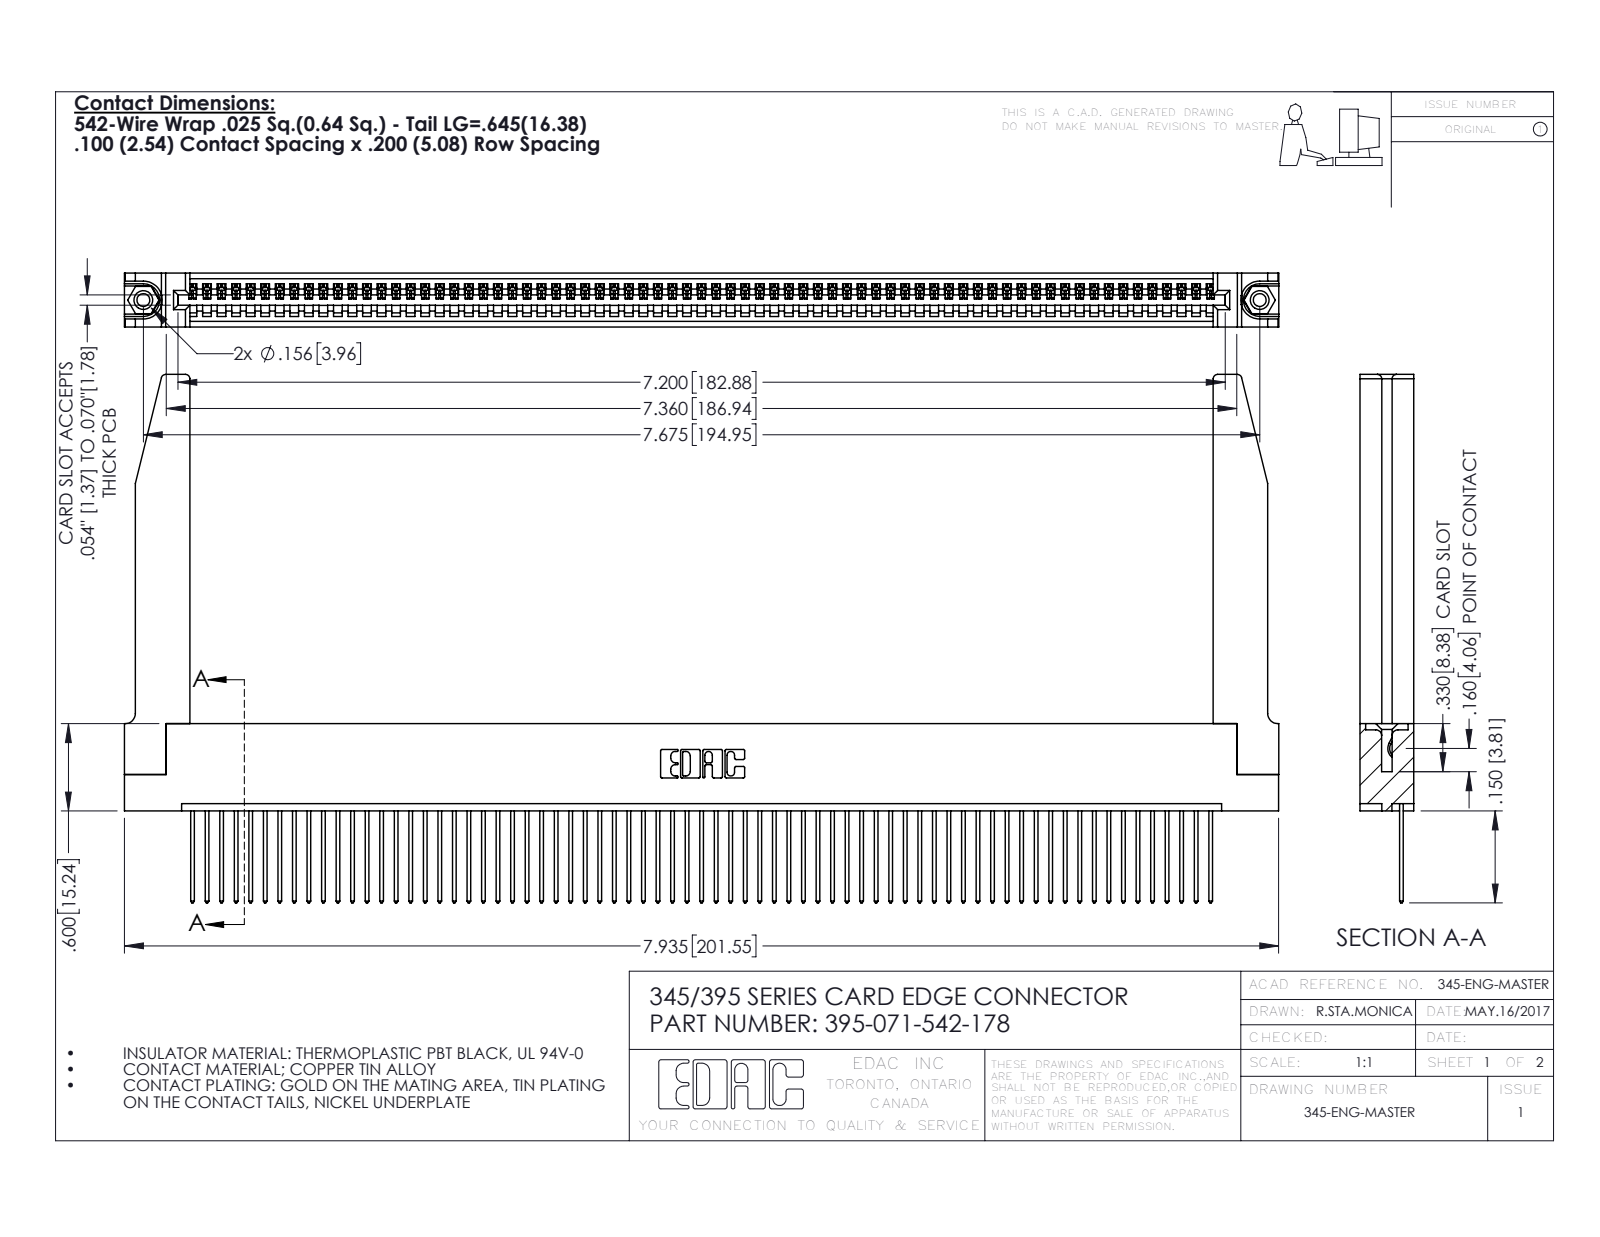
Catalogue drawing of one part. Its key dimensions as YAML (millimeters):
part_name: "345-220-078_345-220-078; 345-250-001_345-250-001-102; 395-071-542-178; 345-292-001_345-293-142 (+1 more)"
step_written_by: "SolidWorks 2016 (CONFIG_CONTROL_DESIGN)"
units: millimeters
bodies: {solids: 76, faces: 4478, planar: 3062, cylindrical: 1364, other: 52}
overall_size: [201.6, 92.3, 9.4]
volume: 27320
surface_area: 34210
round_holes:
  - {diameter: 2.3, count: 2}
  - {diameter: 3.2, count: 2}
  - {diameter: 4, count: 2}
  - {diameter: 1.6, count: 1}
round_bosses_or_shafts:
  - {diameter: 3.9, count: 2}
partial_cylinders:
  - {radius: 0.2, count: 142}
  - {radius: 0.3, count: 142}
  - {radius: 0.3, count: 22}
  - {radius: 0.8, count: 8}
  - {radius: 0.2, count: 6}
  - {radius: 0.8, count: 6}
  - {radius: 0.7, count: 3}
  - {radius: 0.8, count: 2}
face_to_face_distances: [1.8, 7.6, 9.4, 2.5, 6.9, 0.6, 5.1, 5.7, 3.8, 3.8]
hole_center_spacings: [6.9, 189, 194.9]
